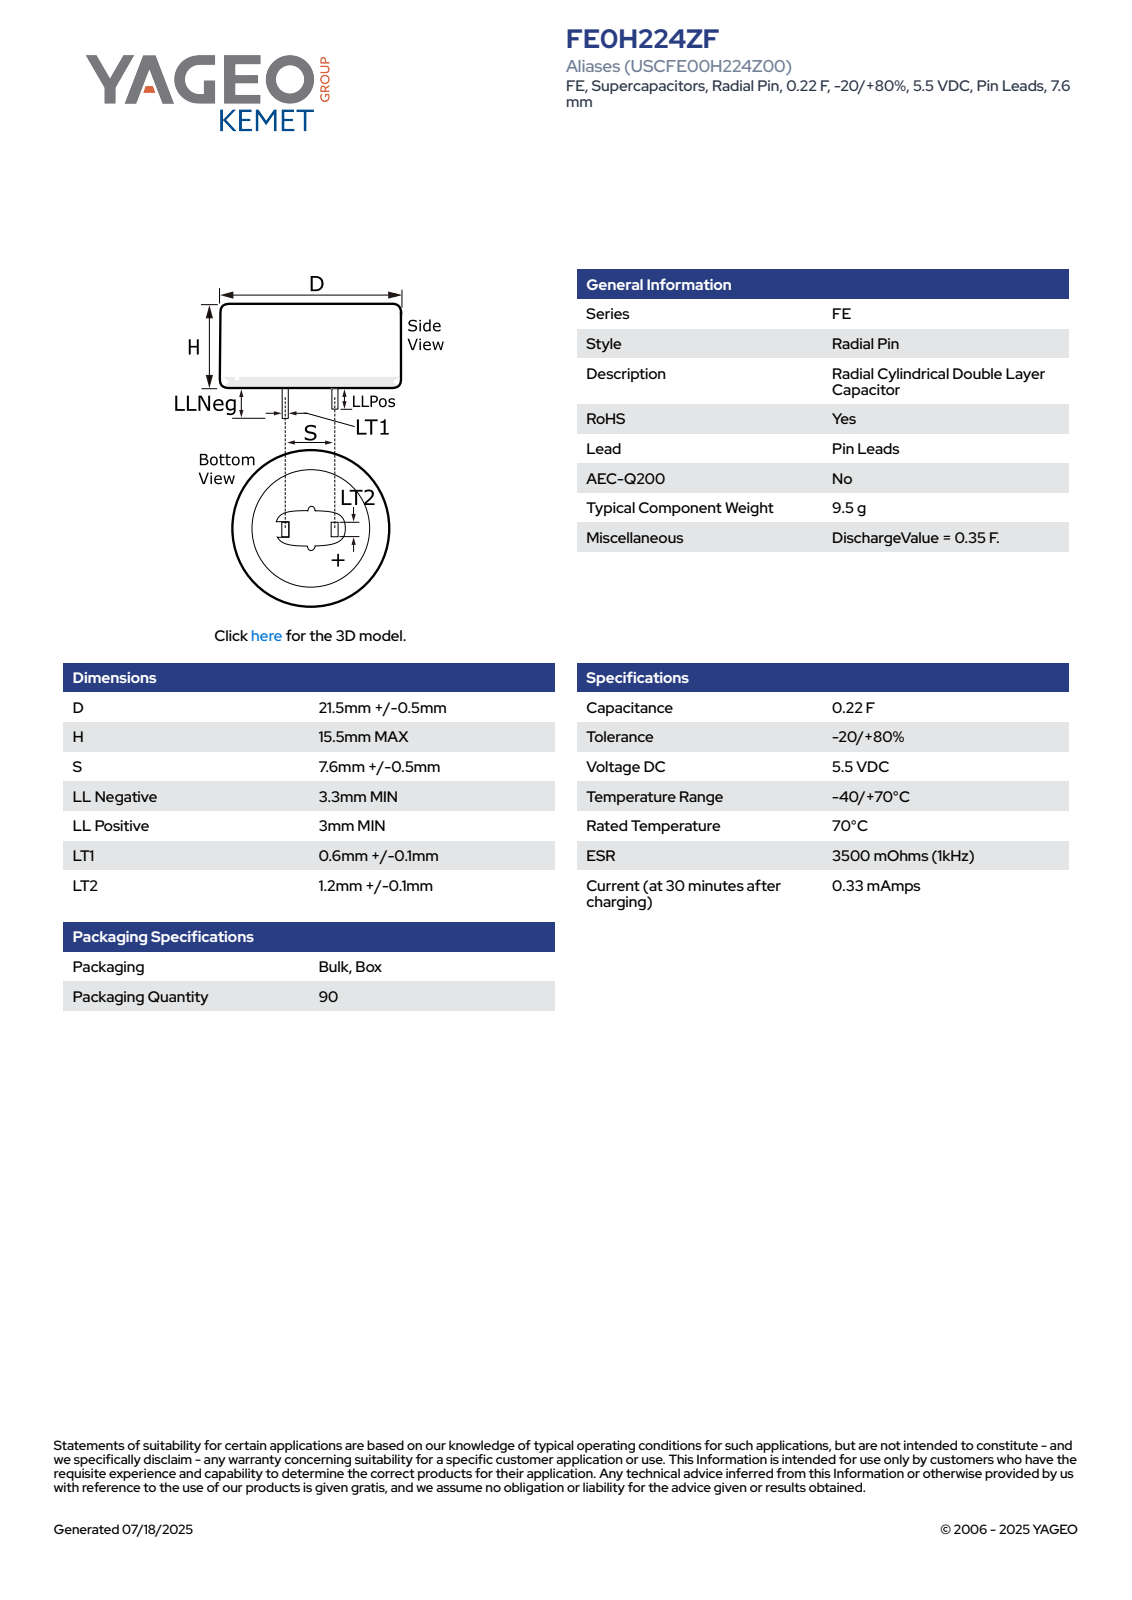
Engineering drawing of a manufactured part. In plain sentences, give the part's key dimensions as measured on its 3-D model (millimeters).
The part is named "CDR_LPLLN_D22L15.5S7.6LLNEG3.3LLPOS3LT10.7LT21.3". Its 3-D file was written by "SolidWorks 2014 (AUTOMOTIVE_DESIGN)". It is 1 solid with 78 faces: 70 planar, 4 cylindrical and 4 other. Overall it measures 22 by 22 by 18.8 millimeters. Its volume is 5 869 cubic millimeters and its surface area 1 797 square millimeters. Round bosses or shafts: 1 of diameter 22. Partial cylindrical surfaces (rounded edges, fillets, slot ends): 1 of radius 11.01. The main face-to-face distances are 15.5, 15.49, 0.7, 7.6, 1.3, 8.3, 6.9, 3.3, 18.79, 18.8.
